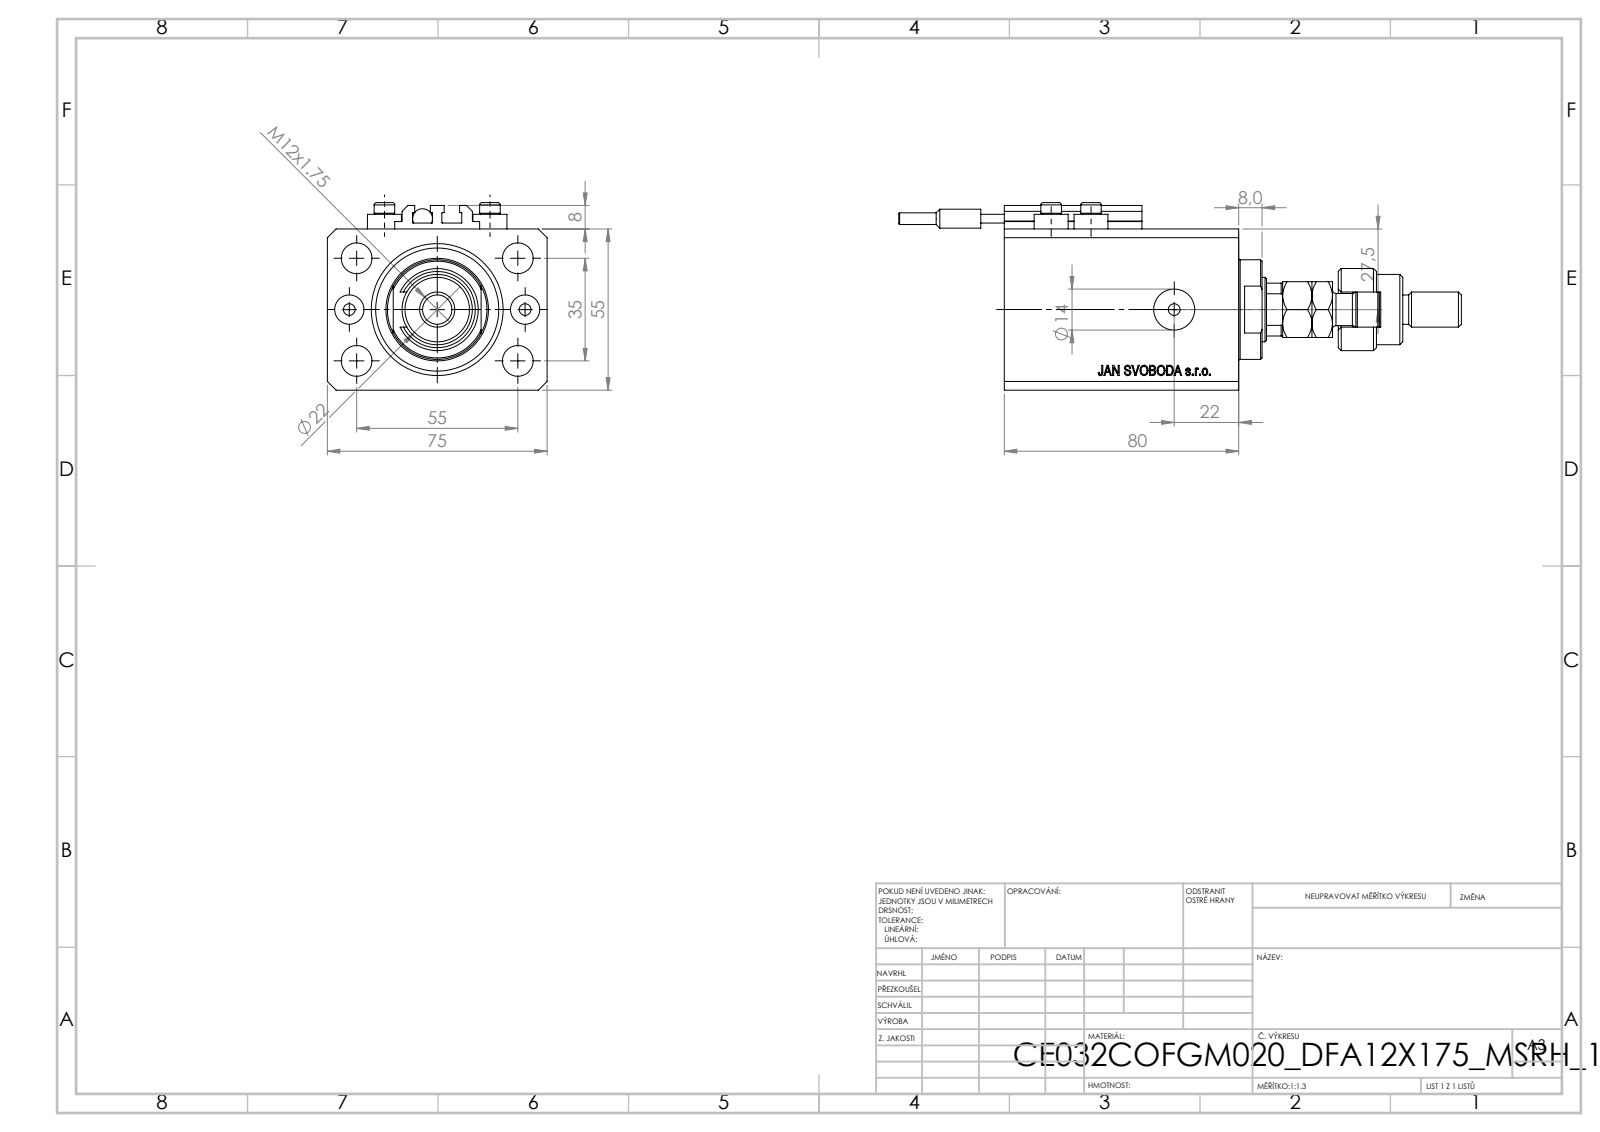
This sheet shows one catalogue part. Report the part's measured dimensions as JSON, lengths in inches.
{"part_name": "V250CE_C_VCP; MFA; FEMALE_PART_FOR_DFA; ALLEN BOLT V250CE (+3 more)", "step_written_by": "SolidWorks 2019 (CONFIG_CONTROL_DESIGN)", "units": "inches", "bodies": {"solids": 11, "faces": 1145, "planar": 548, "cylindrical": 105, "other": 492}, "overall_size": [7.559, 2.953, 2.52], "volume_in3": 19.82, "surface_area_in2": 123.9, "round_holes": [[0.157, 8], [0.413, 5], [0.394, 2], [0.551, 2], [0.866, 1], [1.26, 1], [1.772, 1]], "round_bosses_or_shafts": [[0.457, 4], [0.276, 4], [1.339, 1], [1.102, 1], [0.945, 1], [0.709, 1], [0.472, 1], [0.433, 1]], "partial_cylinders_radius": [[0.008, 10], [0.384, 1], [0.413, 1]], "face_to_face_distances": [2.165, 2.953, 0.591, 3.15, 2.559, 0.39, 2.169, 2.76, 0.118, 0.315], "hole_center_spacings": [0.696, 1.283, 2.366, 1.417, 0.535, 1.181, 1.378, 1.515]}
